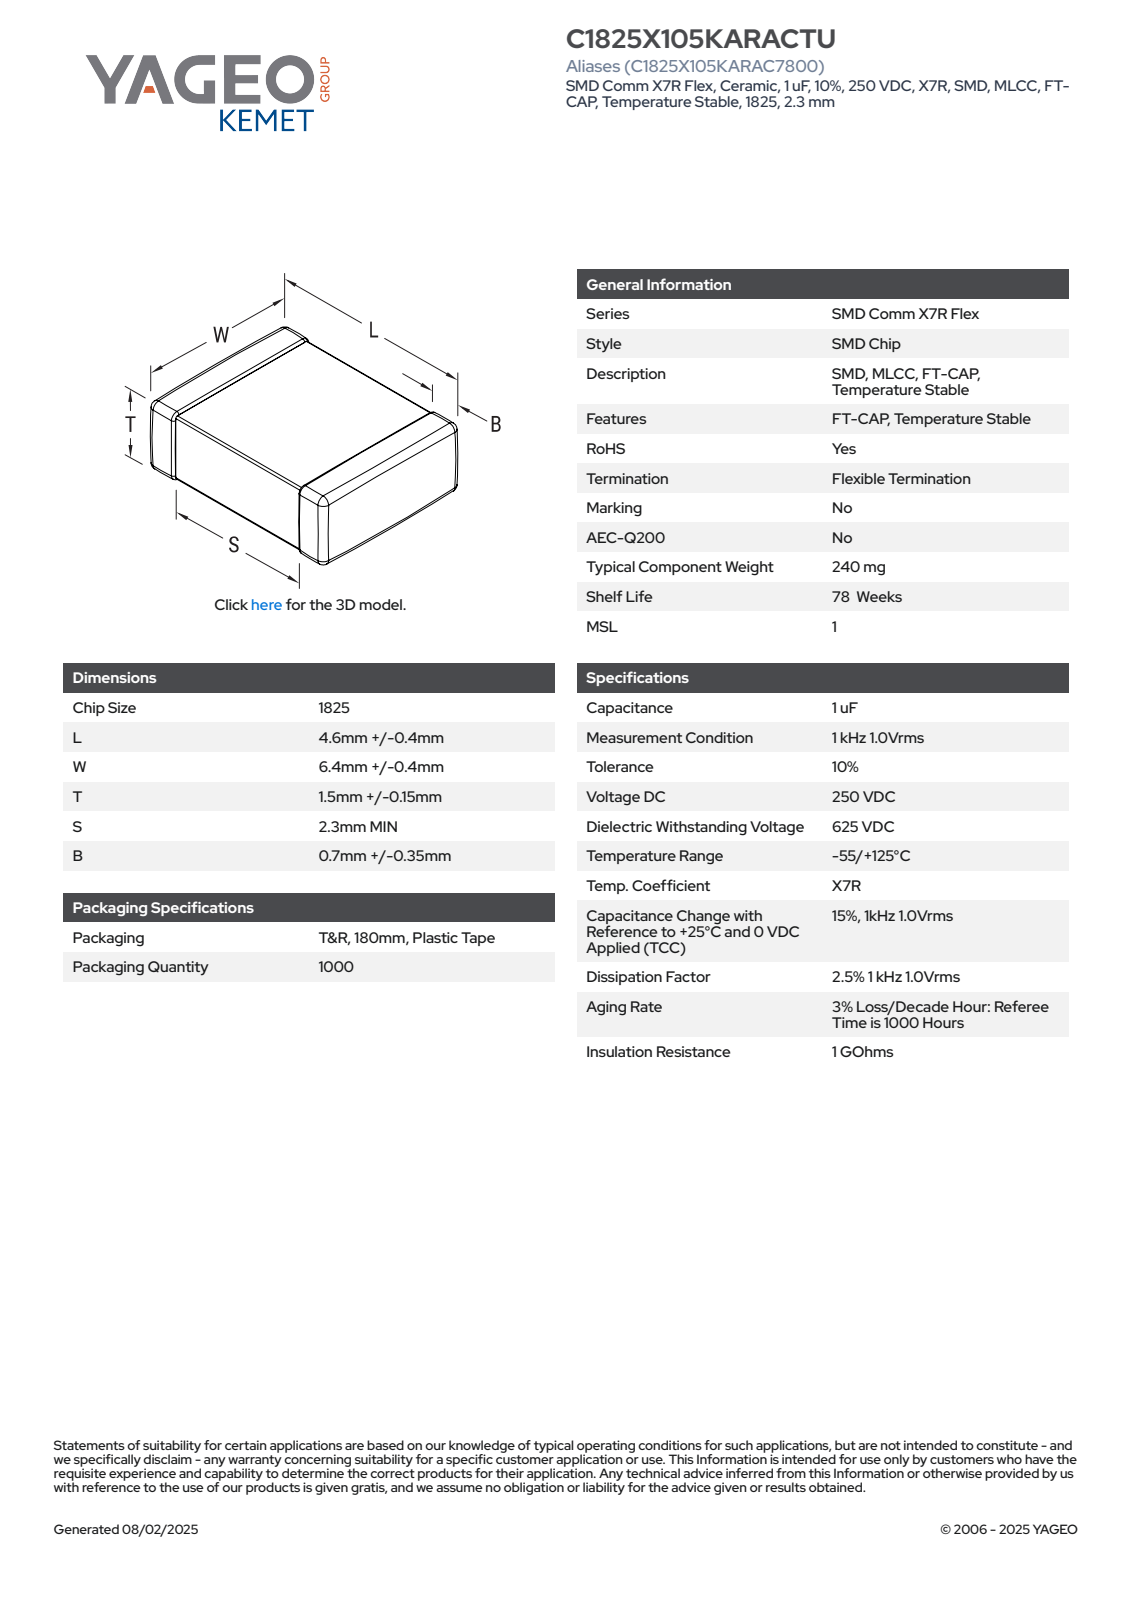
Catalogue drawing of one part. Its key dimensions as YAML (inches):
part_name: "CCS_CCSTD_1825_L5W6.8T1.65B0.7"
step_written_by: "SolidWorks 2021 (AUTOMOTIVE_DESIGN)"
units: inches
bodies: {solids: 4, faces: 125, planar: 71, cylindrical: 38, other: 16}
overall_size: [0.268, 0.197, 0.065]
volume: 0.003
surface_area: 0.169
partial_cylinders:
  - {radius: 0.006, count: 24}
face_to_face_distances: [0.059, 0.054, 0.065, 0.197, 0.262, 0.257, 0.268, 0.039, 0.091, 0.067]
